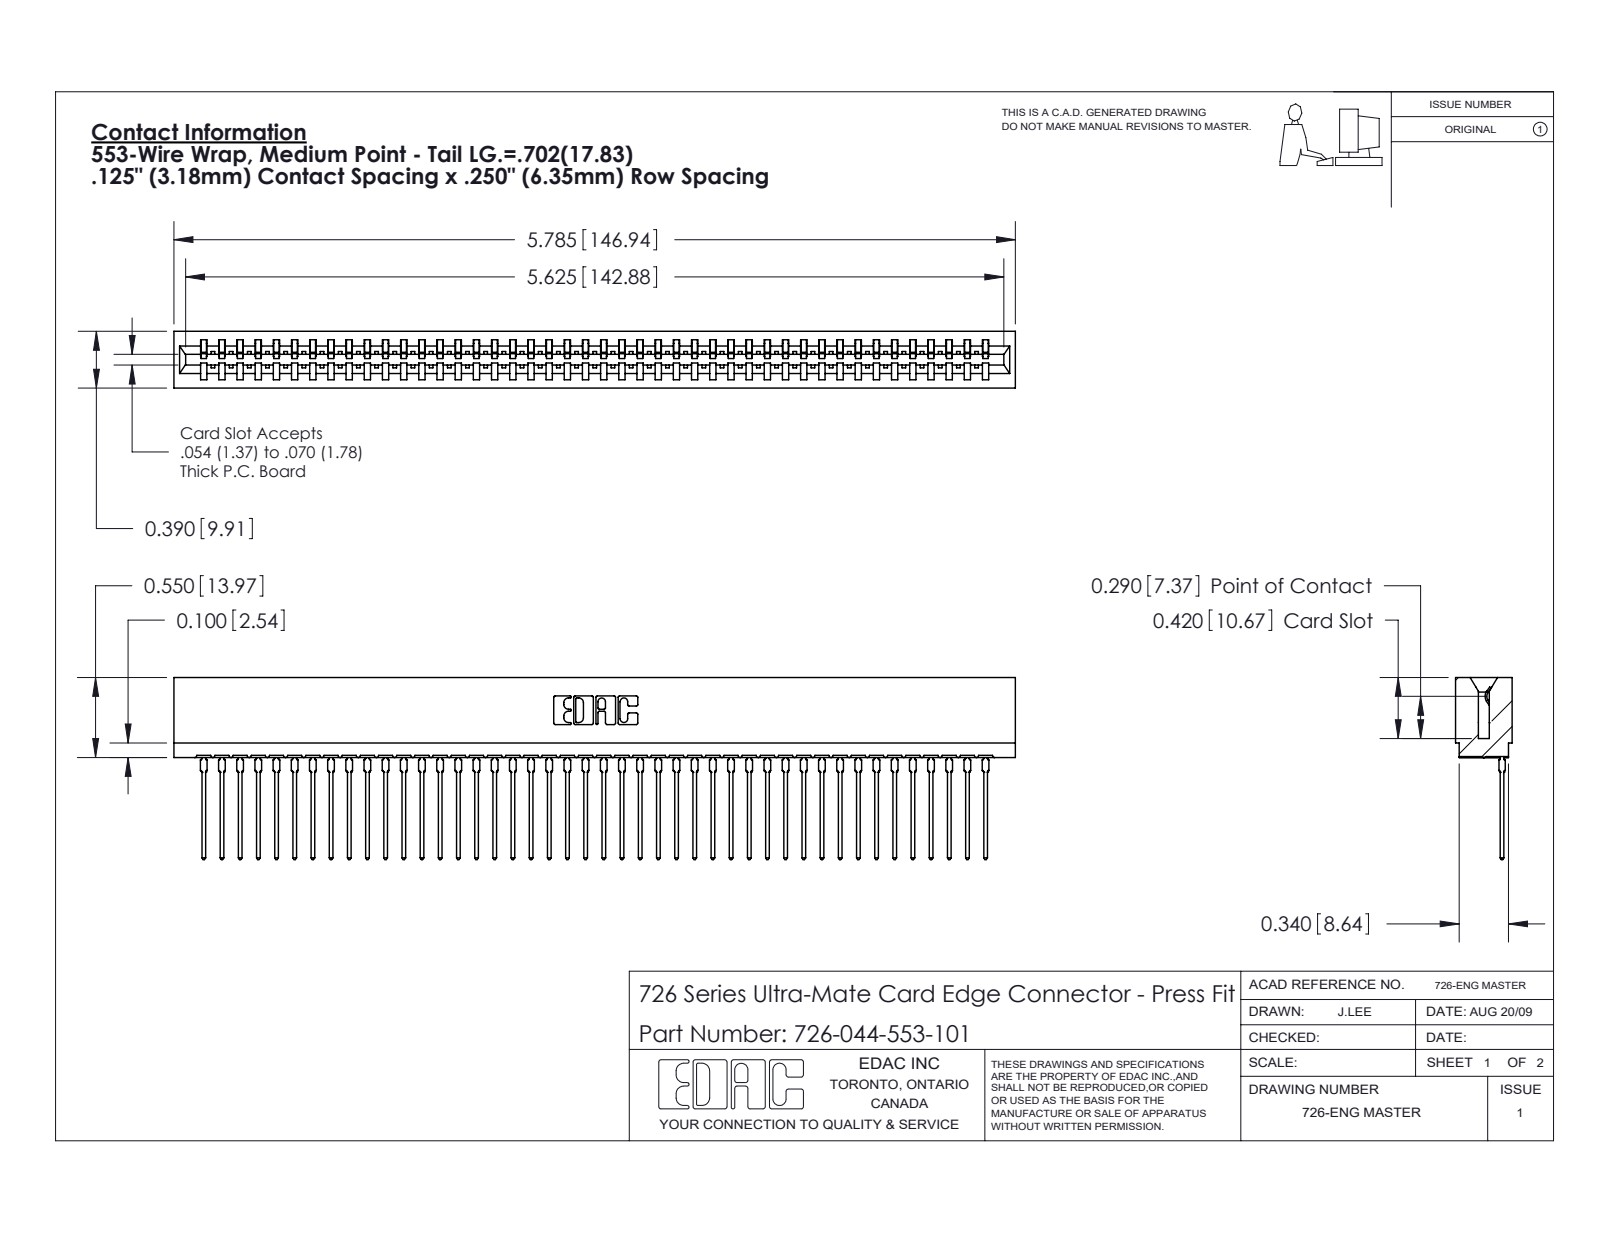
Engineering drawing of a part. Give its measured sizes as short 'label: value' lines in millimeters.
name: 726 Part_.515 Slot Depth - 01; 726-044-553-101; 746-292-001_553
written by: SolidWorks 2020 (CONFIG_CONTROL_DESIGN)
unit: mm
bodies: 45 solids, 4849 faces (2827 planar, 878 cylindrical, 1144 other)
size: 146.9 × 31.8 × 9.9
volume: 13 300 mm³; area: 21 100 mm²
rounds: 88× R0.5, 45× R0.4, 22× R0.3, 6× R0.2, 6× R0.8, 4× R0.1, 4× R0.3, 3× R0.7
face distances: 1.4, 8.5, 9.9, 0.6, 7.8, 6.4, 2.1, 7, 9.3, 0.8
